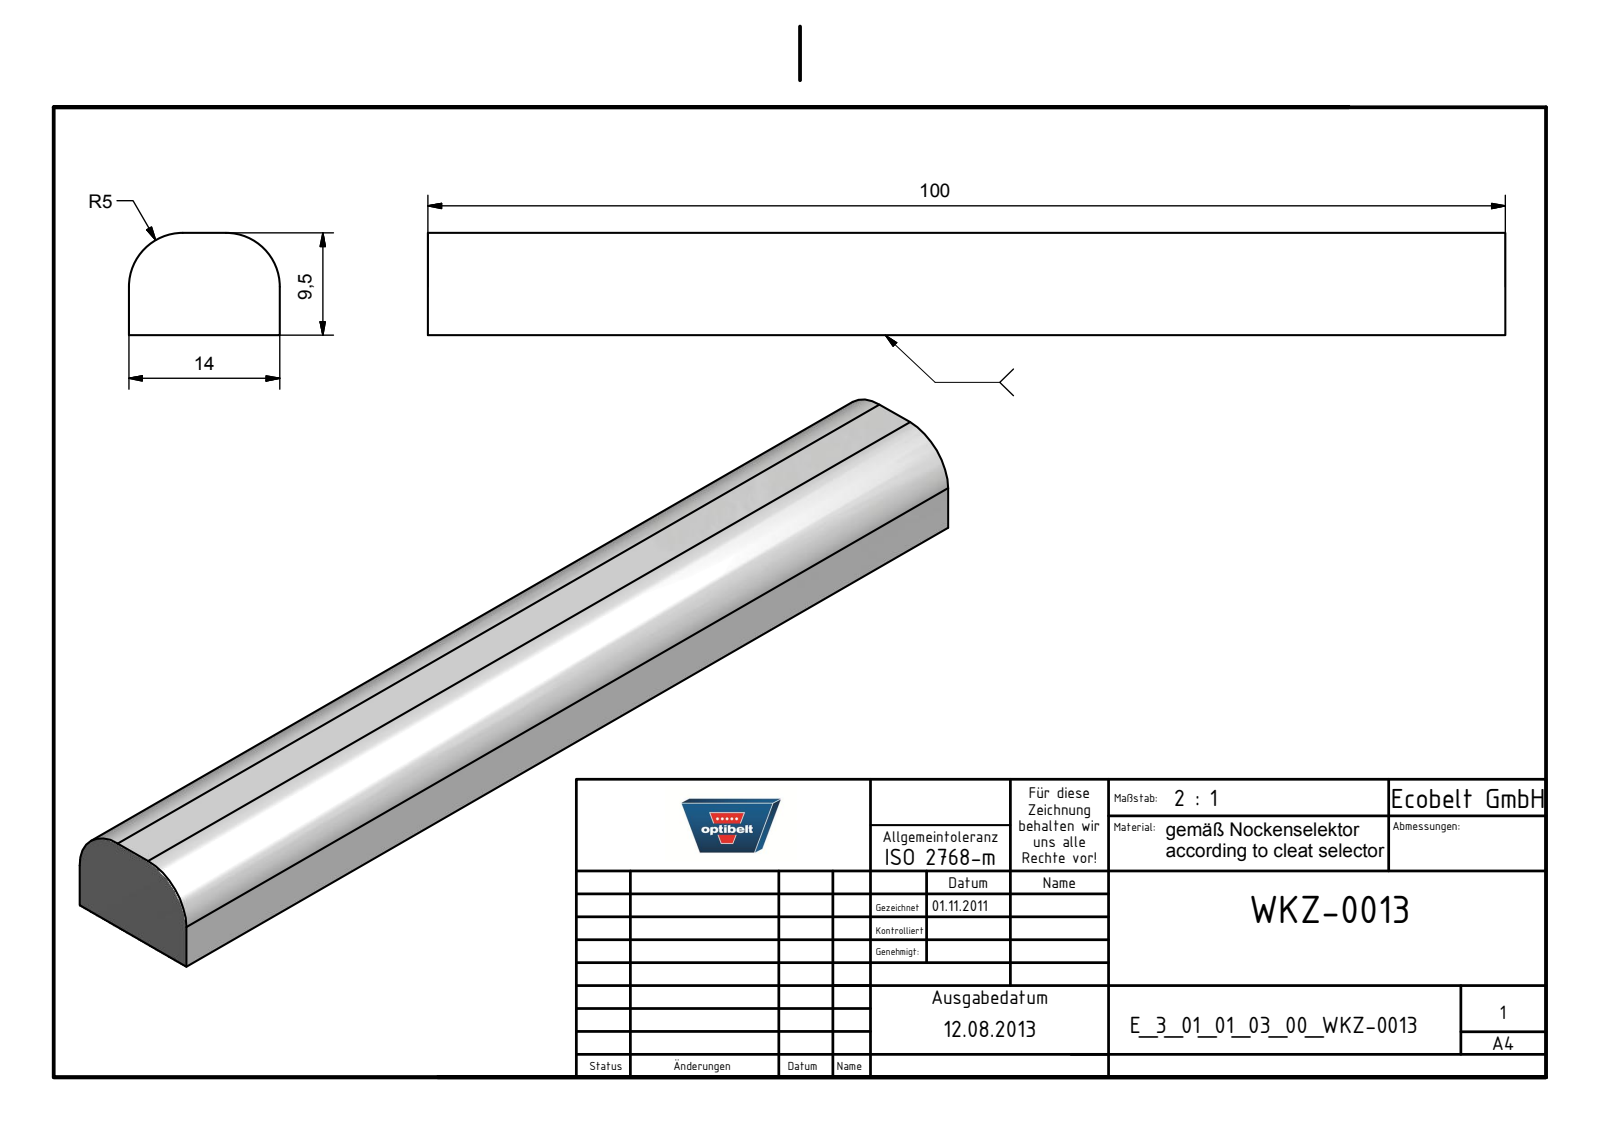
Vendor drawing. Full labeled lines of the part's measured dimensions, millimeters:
Part name (STEP PRODUCT): E_3_01_01_03_00_WKZ-0013
STEP written by: Autodesk Inventor 2021 (AUTOMOTIVE_DESIGN)
Units: millimetres
Bodies: 1 solid, 8 faces (6 planar, 2 cylindrical, 0 other)
Overall size (bounding box): 100 × 14 × 9.5
Volume: 12 227 mm³ · Surface area: 4 515 mm²
Partial cylindrical surfaces — rounded edges, fillets, slot ends (radius × count): R5 ×2
Main face-to-face distances: 14, 9.5, 100
